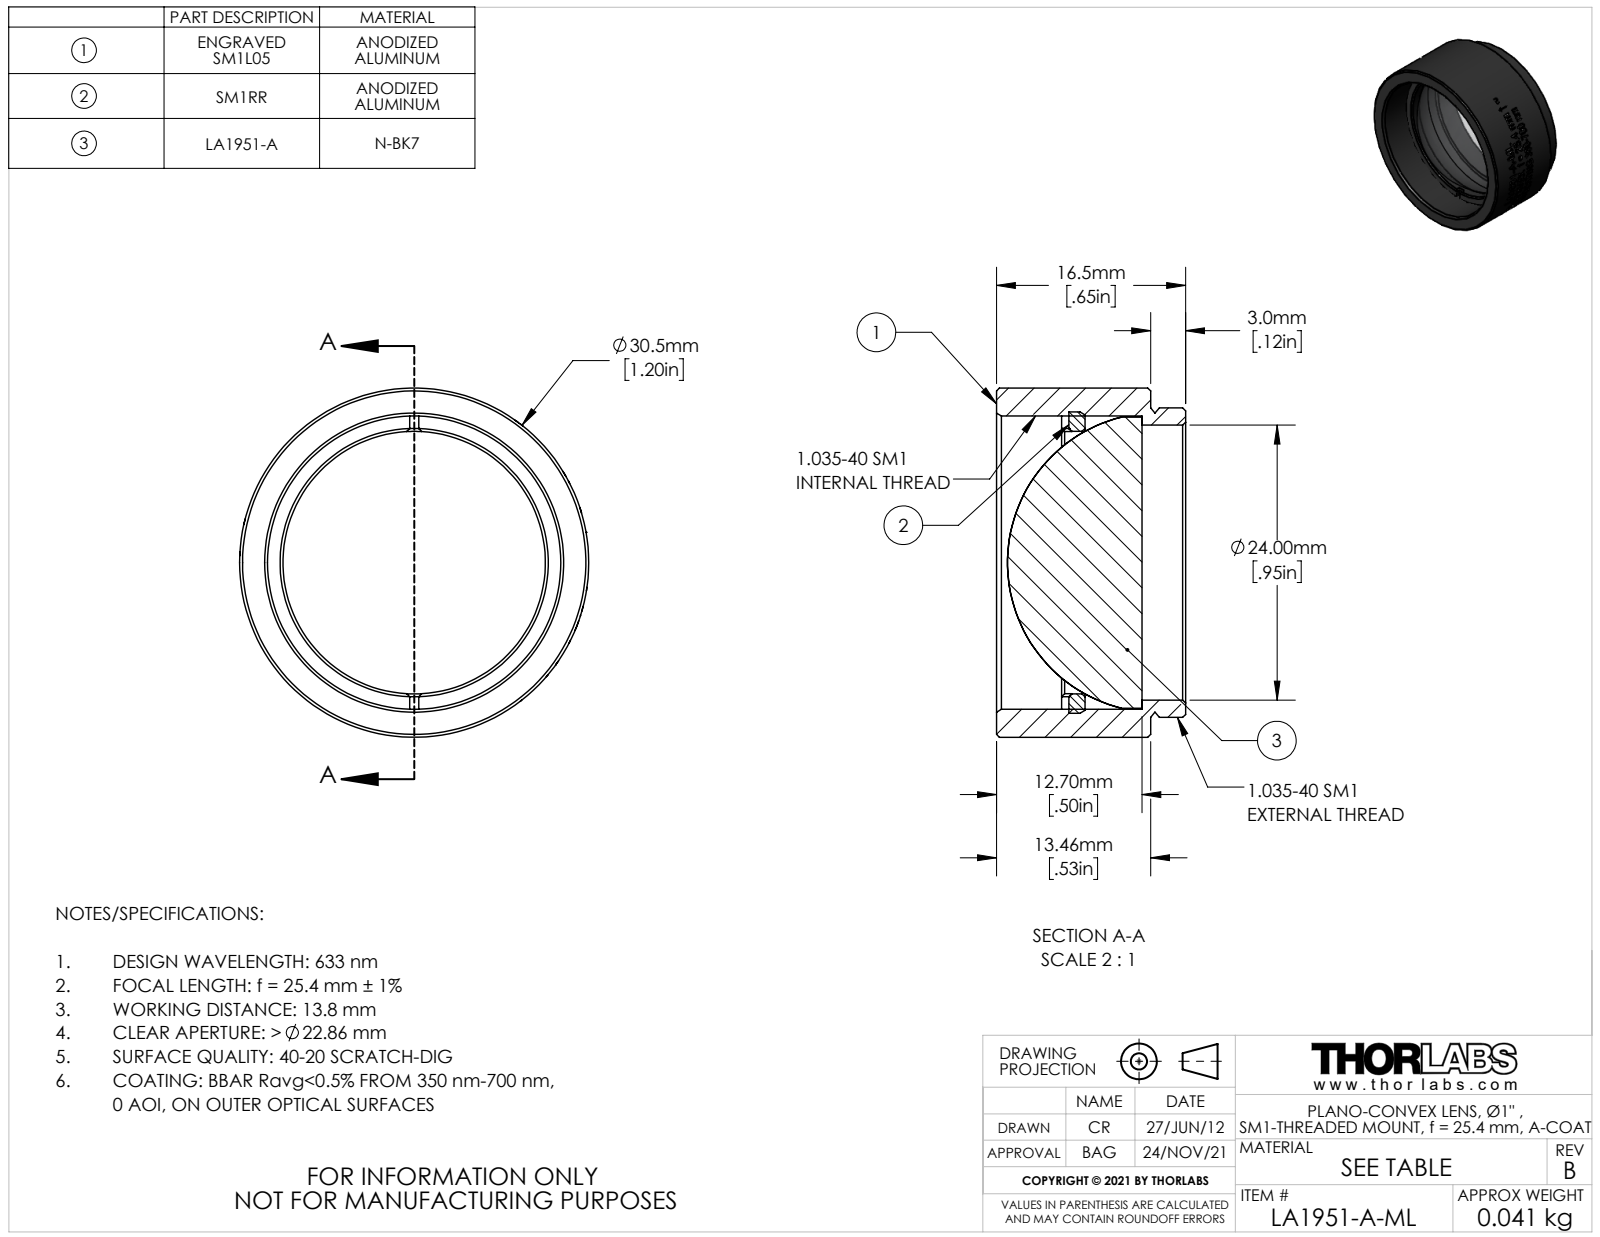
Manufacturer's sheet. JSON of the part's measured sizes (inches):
{"part_name": "24415-999", "step_written_by": "SolidWorks 2018 (AUTOMOTIVE_DESIGN)", "units": "inches", "bodies": {"solids": 3, "faces": 861, "planar": 339, "cylindrical": 106, "other": 416}, "overall_size": [1.2, 1.2, 0.65], "volume_in3": 0.456, "surface_area_in2": 8.331, "round_holes": [[0.902, 1], [0.945, 1], [1.008, 1]], "round_bosses_or_shafts": [[1.2, 1], [1.063, 1], [1.035, 1], [1, 1]], "partial_cylinders_radius": [[0.6, 1]], "face_to_face_distances": [0.5, 0.03, 0.53, 0.226, 0.196, 0.304, 0.08, 0.306, 0.276, 0.224]}
